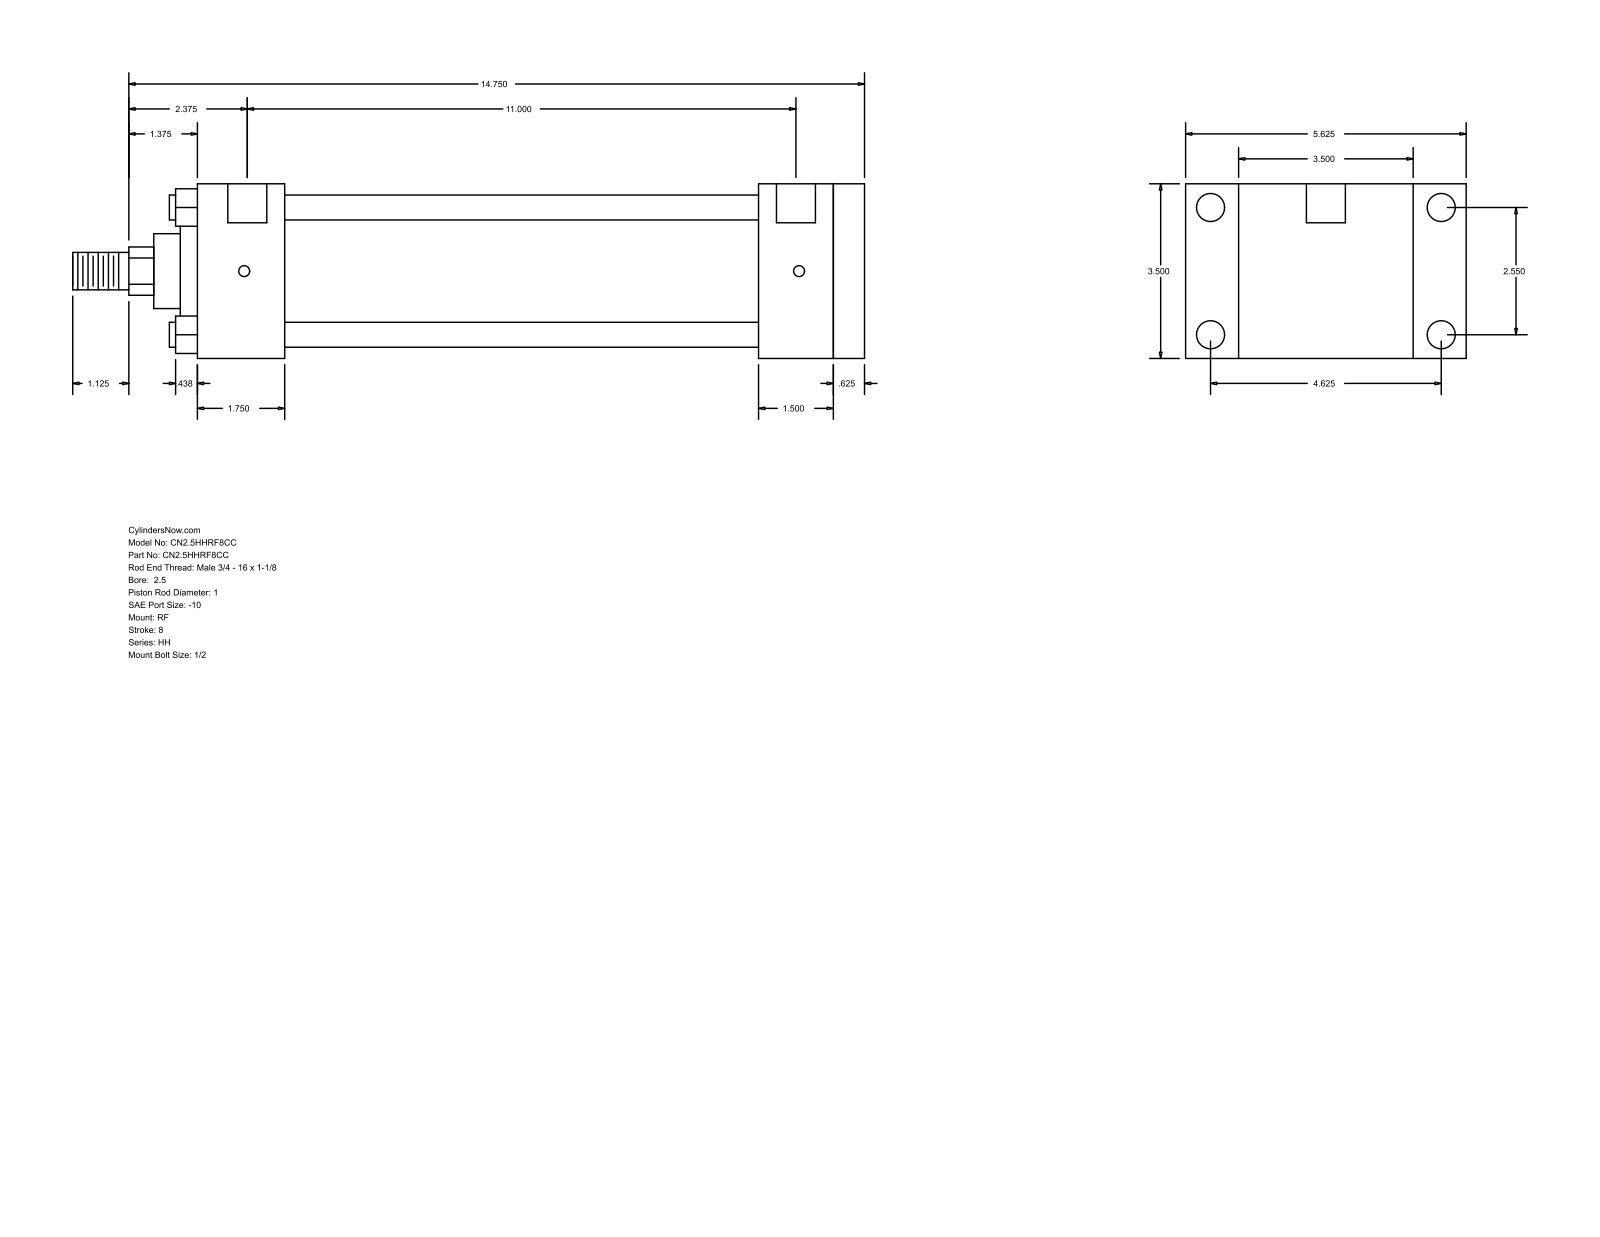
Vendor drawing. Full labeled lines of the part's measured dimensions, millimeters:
Part name (STEP PRODUCT): HH_RF__0250_1
STEP written by: GSSL Pune (CONFIG_CONTROL_DESIGN)
Units: millimetres
Bodies: 0 solids, 94 faces (65 planar, 29 cylindrical, 0 other)
Overall size (bounding box): 403.23 × 142.88 × 88.9
Round holes (diameter × count): ⌀5.56 ×4, ⌀14.3 ×4, ⌀19.84 ×2
Round bosses / shafts (diameter × count): ⌀12.7 ×4, ⌀73.03 ×1, ⌀60.33 ×1, ⌀38.1 ×1, ⌀25.4 ×1, ⌀19.05 ×1
Partial cylindrical surfaces — rounded edges, fillets, slot ends (radius × count): R12.29 ×1
Main face-to-face distances: 88.9, 15.88, 323.85, 339.73, 44.46, 279.39, 295.27, 285.76, 241.3, 38.09
Hole centre spacings: 64.76, 117.48, 134.15, 282.57, 1.58, 1.59, 279.4, 280.98
